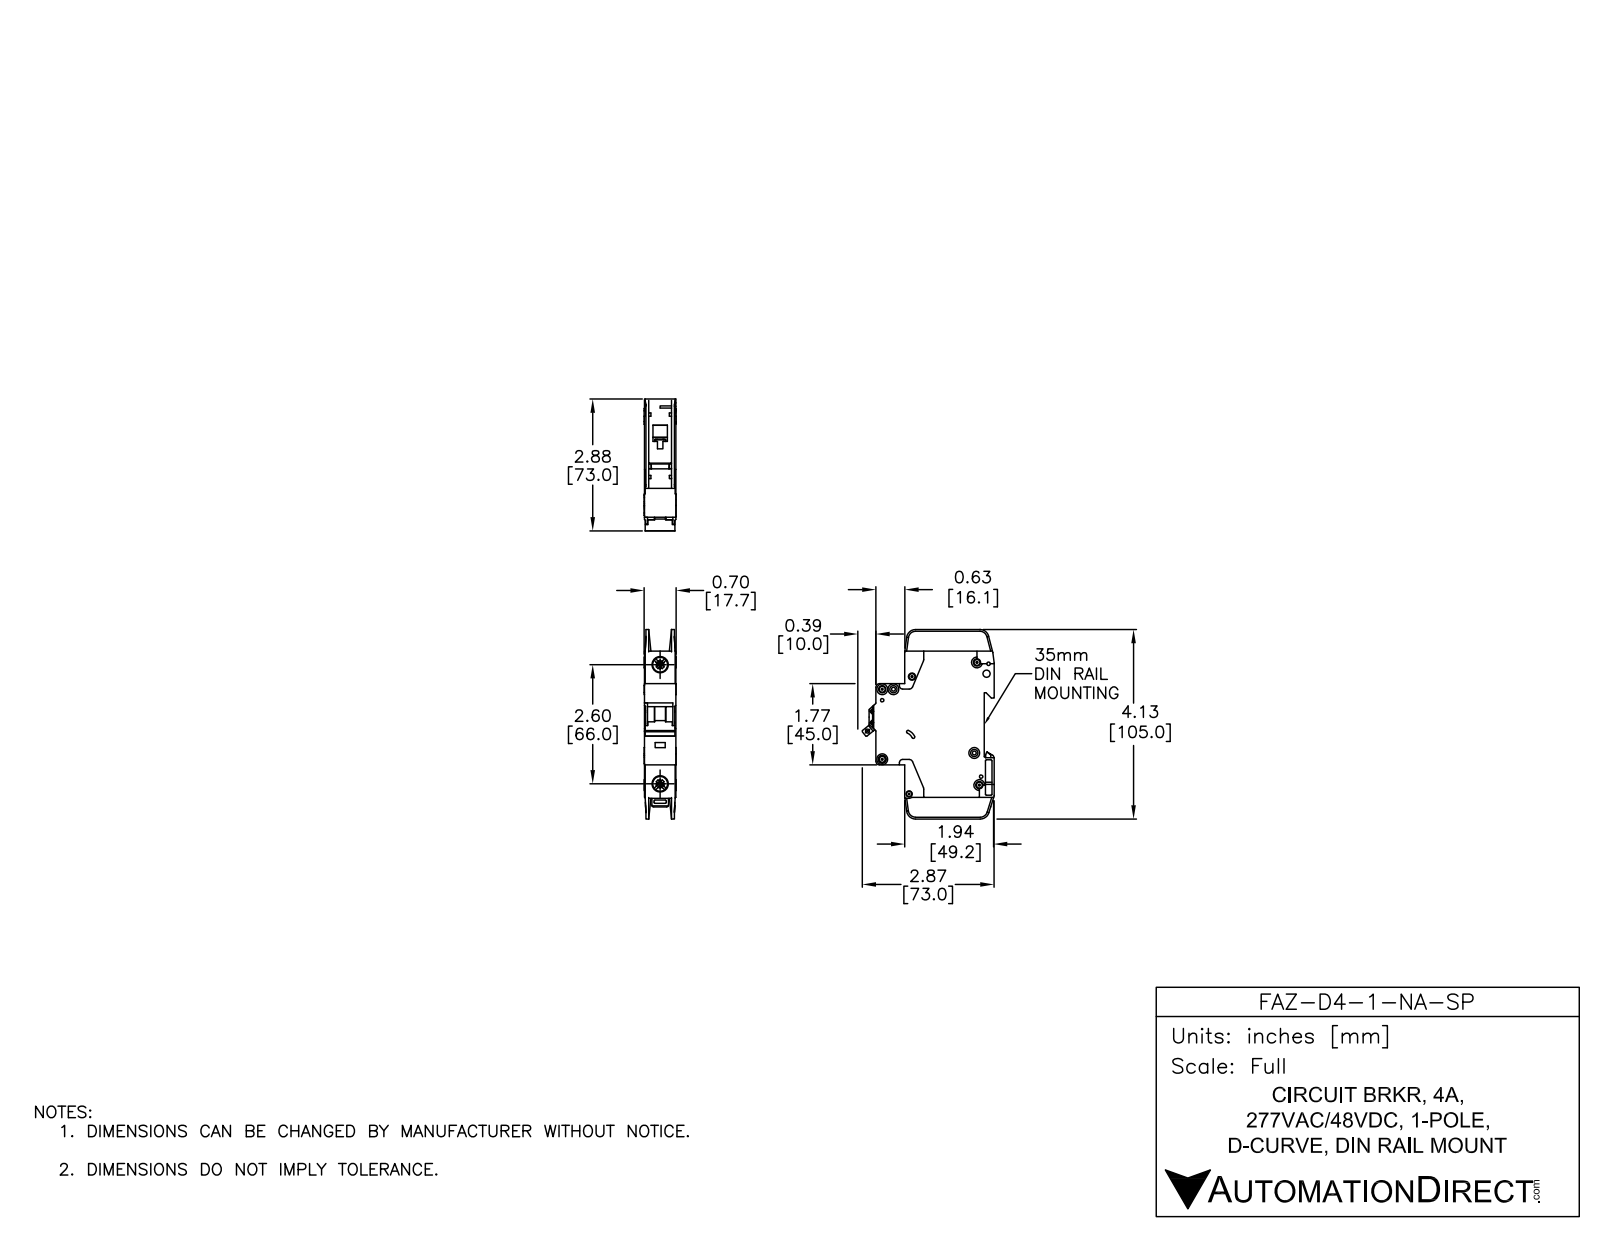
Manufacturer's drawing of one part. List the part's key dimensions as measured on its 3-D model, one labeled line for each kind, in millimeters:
Part name (STEP PRODUCT): FAZ-D4-1-NA-SP
STEP written by: SolidWorks 2014 (AUTOMOTIVE_DESIGN)
Units: millimetres
Bodies: 3 solids, 784 faces (409 planar, 263 cylindrical, 112 other)
Overall size (bounding box): 105 × 73.04 × 17.7
Volume: 77 695 mm³ · Surface area: 24 740 mm²
Round holes (diameter × count): ⌀3.6 ×7, ⌀1.09 ×2, ⌀1.5 ×2, ⌀4 ×2, ⌀7.15 ×2, ⌀8.2 ×2, ⌀1.9 ×1, ⌀2.15 ×1, ⌀2.2 ×1, ⌀2.55 ×1, ⌀3.3 ×1, ⌀3.4 ×1
Round bosses / shafts (diameter × count): ⌀6 ×7, ⌀2.5 ×1
Partial cylindrical surfaces — rounded edges, fillets, slot ends (radius × count): R0.25 ×29, R0.5 ×18, R1 ×10, R2 ×10, R5 ×5, R4 ×4, R1.8 ×3, R0.2 ×2
Main face-to-face distances: 17.5, 15.05, 0.7, 2.45, 1.75, 15.75, 13.3, 14, 12.6, 2
Hole centre spacings: 6.2, 5.19, 6.1, 8.19, 8.56, 8.7, 11.11, 12.45
